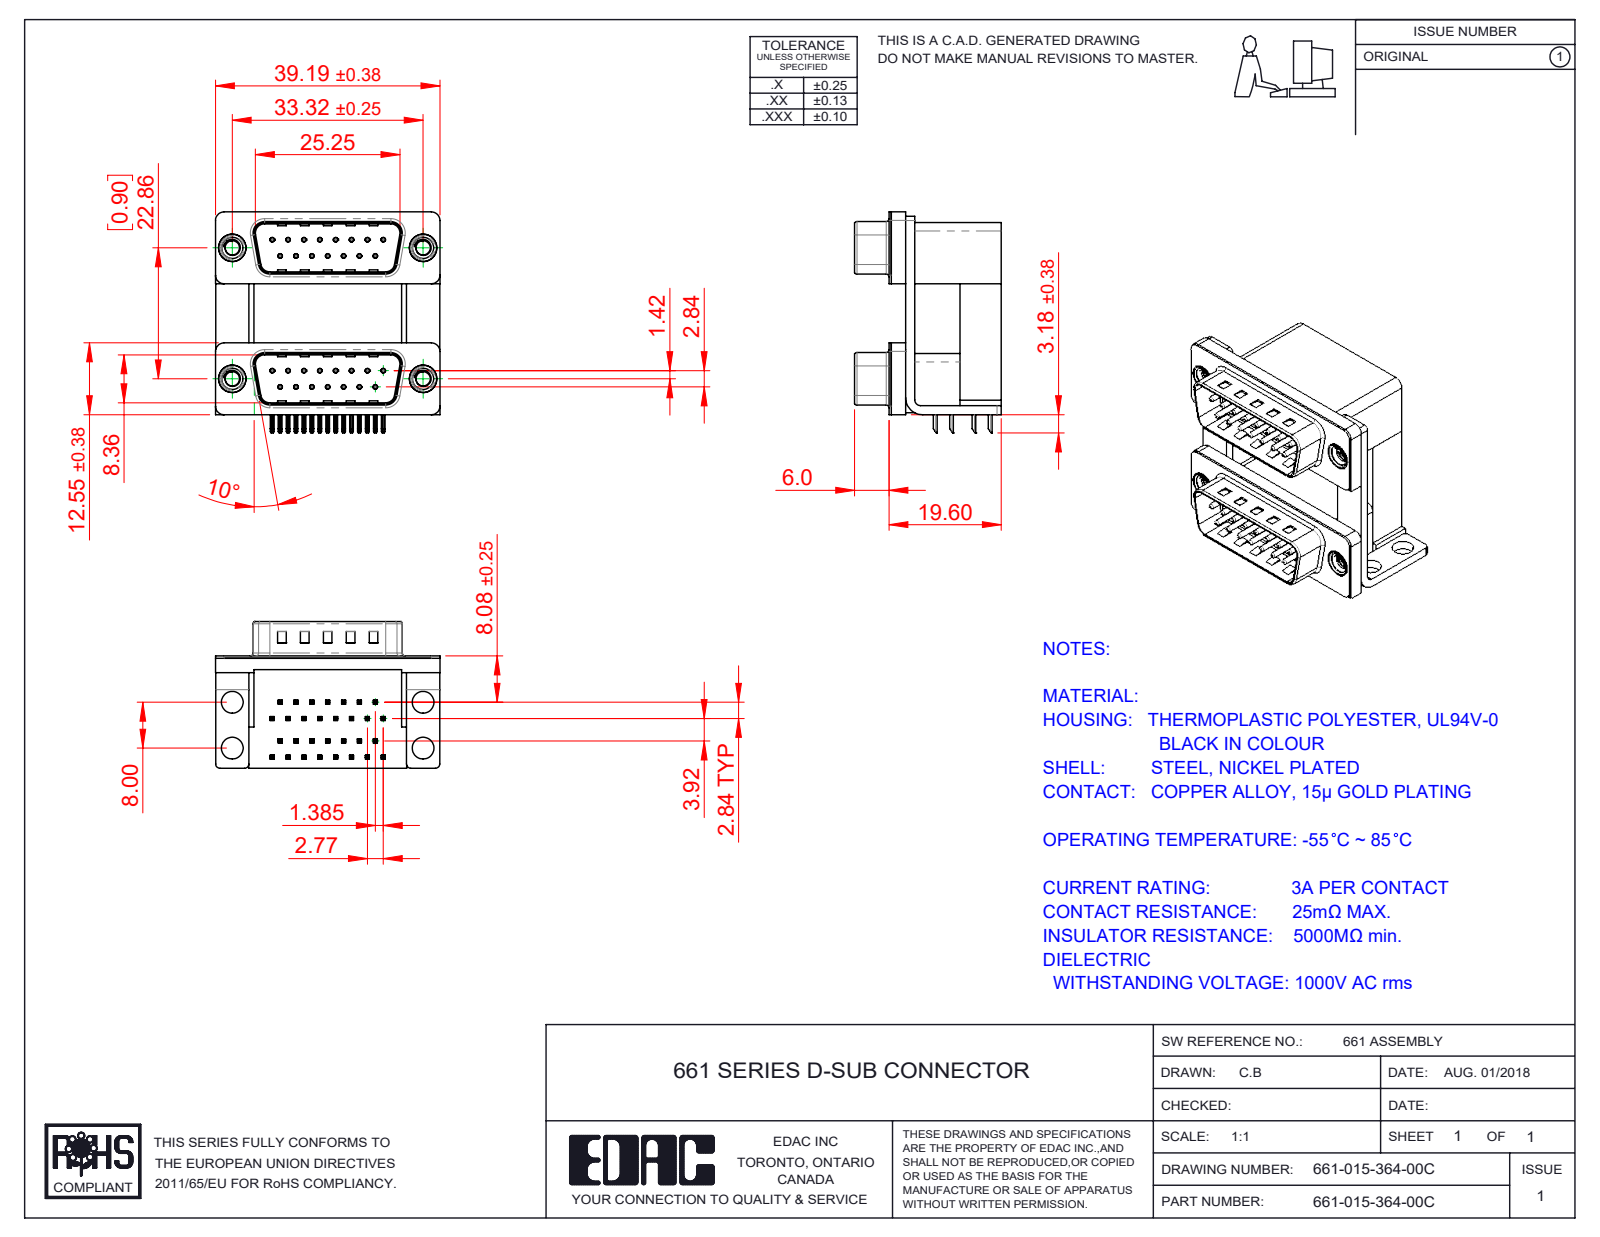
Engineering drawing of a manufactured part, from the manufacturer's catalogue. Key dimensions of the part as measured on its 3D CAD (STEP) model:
Part name (STEP PRODUCT): 661 Housing Lower_15 Contacts; 661-015-364-00C; 661 Contact Top Upper_H; 661 Contact Bottom Upper_H (+7 more)
STEP written by: SolidWorks 2020 (CONFIG_CONTROL_DESIGN)
Units: millimetres
Bodies: 41 solids, 2966 faces (1834 planar, 862 cylindrical, 270 other)
Overall size (bounding box): 39.19 × 38.59 × 25.6
Volume: 15 127 mm³ · Surface area: 16 327 mm²
Round holes (diameter × count): ⌀0.35 ×30, ⌀0.8 ×30, ⌀2.5 ×4, ⌀3.5 ×4, ⌀3.8 ×4, ⌀4 ×4, ⌀4.8 ×4, ⌀5 ×4
Round bosses / shafts (diameter × count): ⌀0.75 ×30, ⌀4.9 ×4, ⌀4.75 ×4, ⌀3.9 ×4
Partial cylindrical surfaces — rounded edges, fillets, slot ends (radius × count): R0.25 ×120, R0.12 ×60, R0.5 ×16, R1.5 ×15, R0.75 ×8, R0.9 ×8, R1.6 ×8, R2 ×8
Main face-to-face distances: 0.4, 12, 22.86, 19.2, 7.2, 16.7, 9.5, 2.5, 12.4, 10.7
Hole centre spacings: 3.16, 2.77, 23.03, 5.54, 23.52, 8.31, 22.86, 24.32
